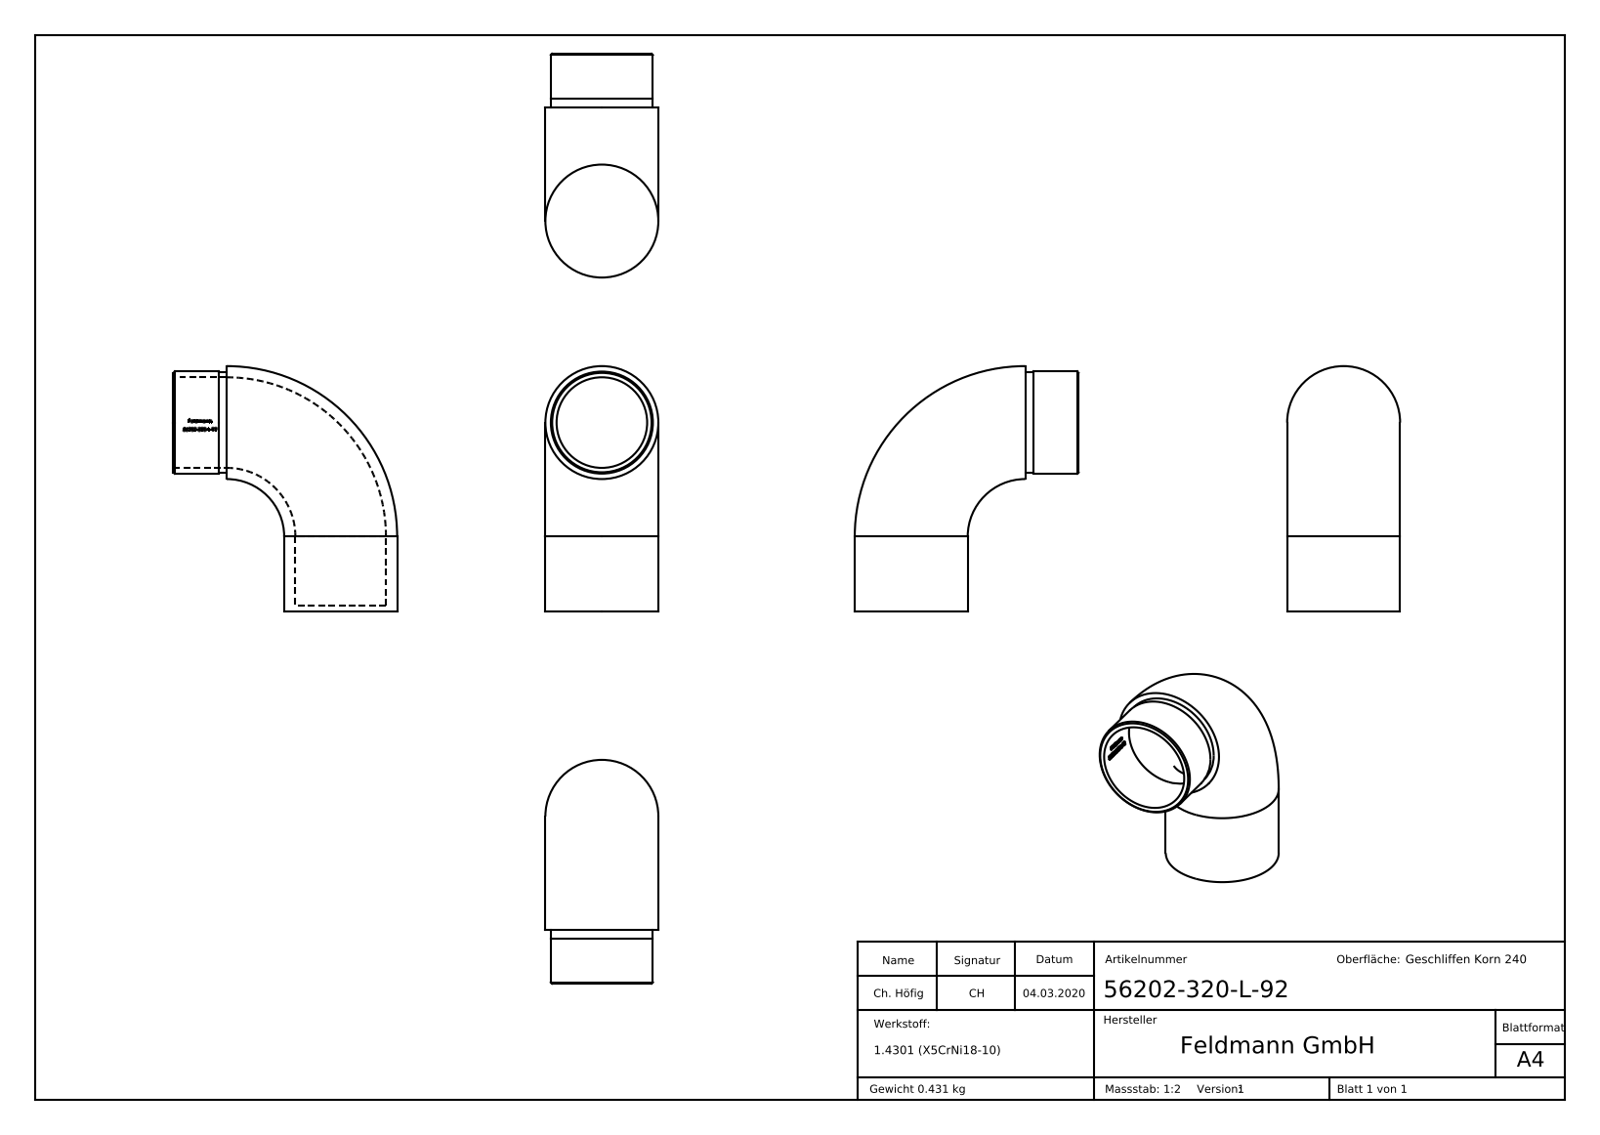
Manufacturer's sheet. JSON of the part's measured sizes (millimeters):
{"part_name": "56202-320-L-92", "step_written_by": "SolidWorks 2015 (CONFIG_CONTROL_DESIGN)", "units": "millimeters", "bodies": {"solids": 1, "faces": 283, "planar": 116, "cylindrical": 34, "other": 133}, "overall_size": [92, 84, 42.4], "volume_mm3": 54611, "surface_area_mm2": 30030, "round_holes": [[34, 2]], "round_bosses_or_shafts": [[42.4, 1], [38.3, 1], [37.9, 1]], "partial_cylinders_radius": [[17.1, 1]], "face_to_face_distances": [2, 20, 3, 17, 67.6, 65.6, 0.44, 67.73, 65.73, 2.97]}
